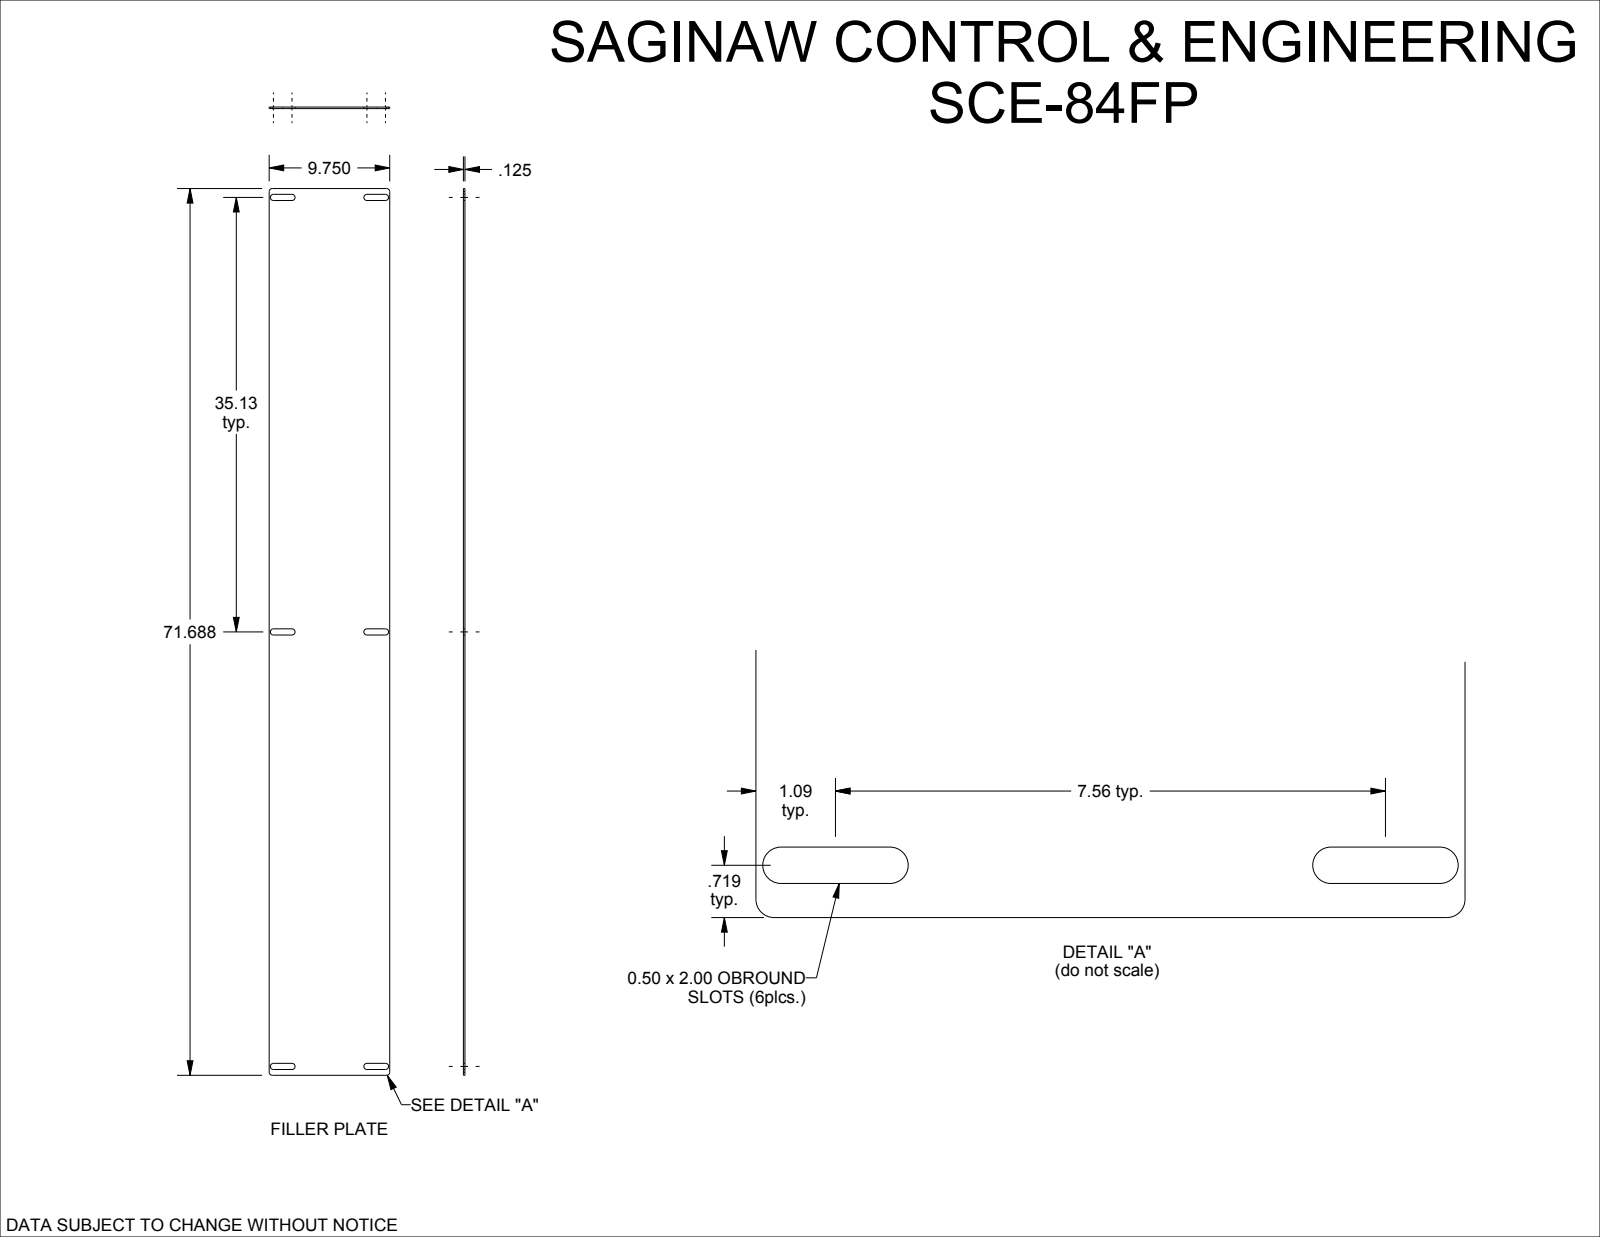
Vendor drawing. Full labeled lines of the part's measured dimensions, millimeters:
Part name (STEP PRODUCT): SCE-84FP
STEP written by: SolidWorks 2023 (AUTOMOTIVE_DESIGN)
Units: millimetres
Bodies: 1 solid, 46 faces (30 planar, 16 cylindrical, 0 other)
Overall size (bounding box): 1820.8 × 247.7 × 3.2
Volume: 1 420 000 mm³ · Surface area: 909 700 mm²
Partial cylindrical surfaces — rounded edges, fillets, slot ends (radius × count): R6.4 ×16
Main face-to-face distances: 3.2, 247.7, 892.2, 1820.8, 12.7, 904.1, 916.8, 11.9, 1809, 24.6
